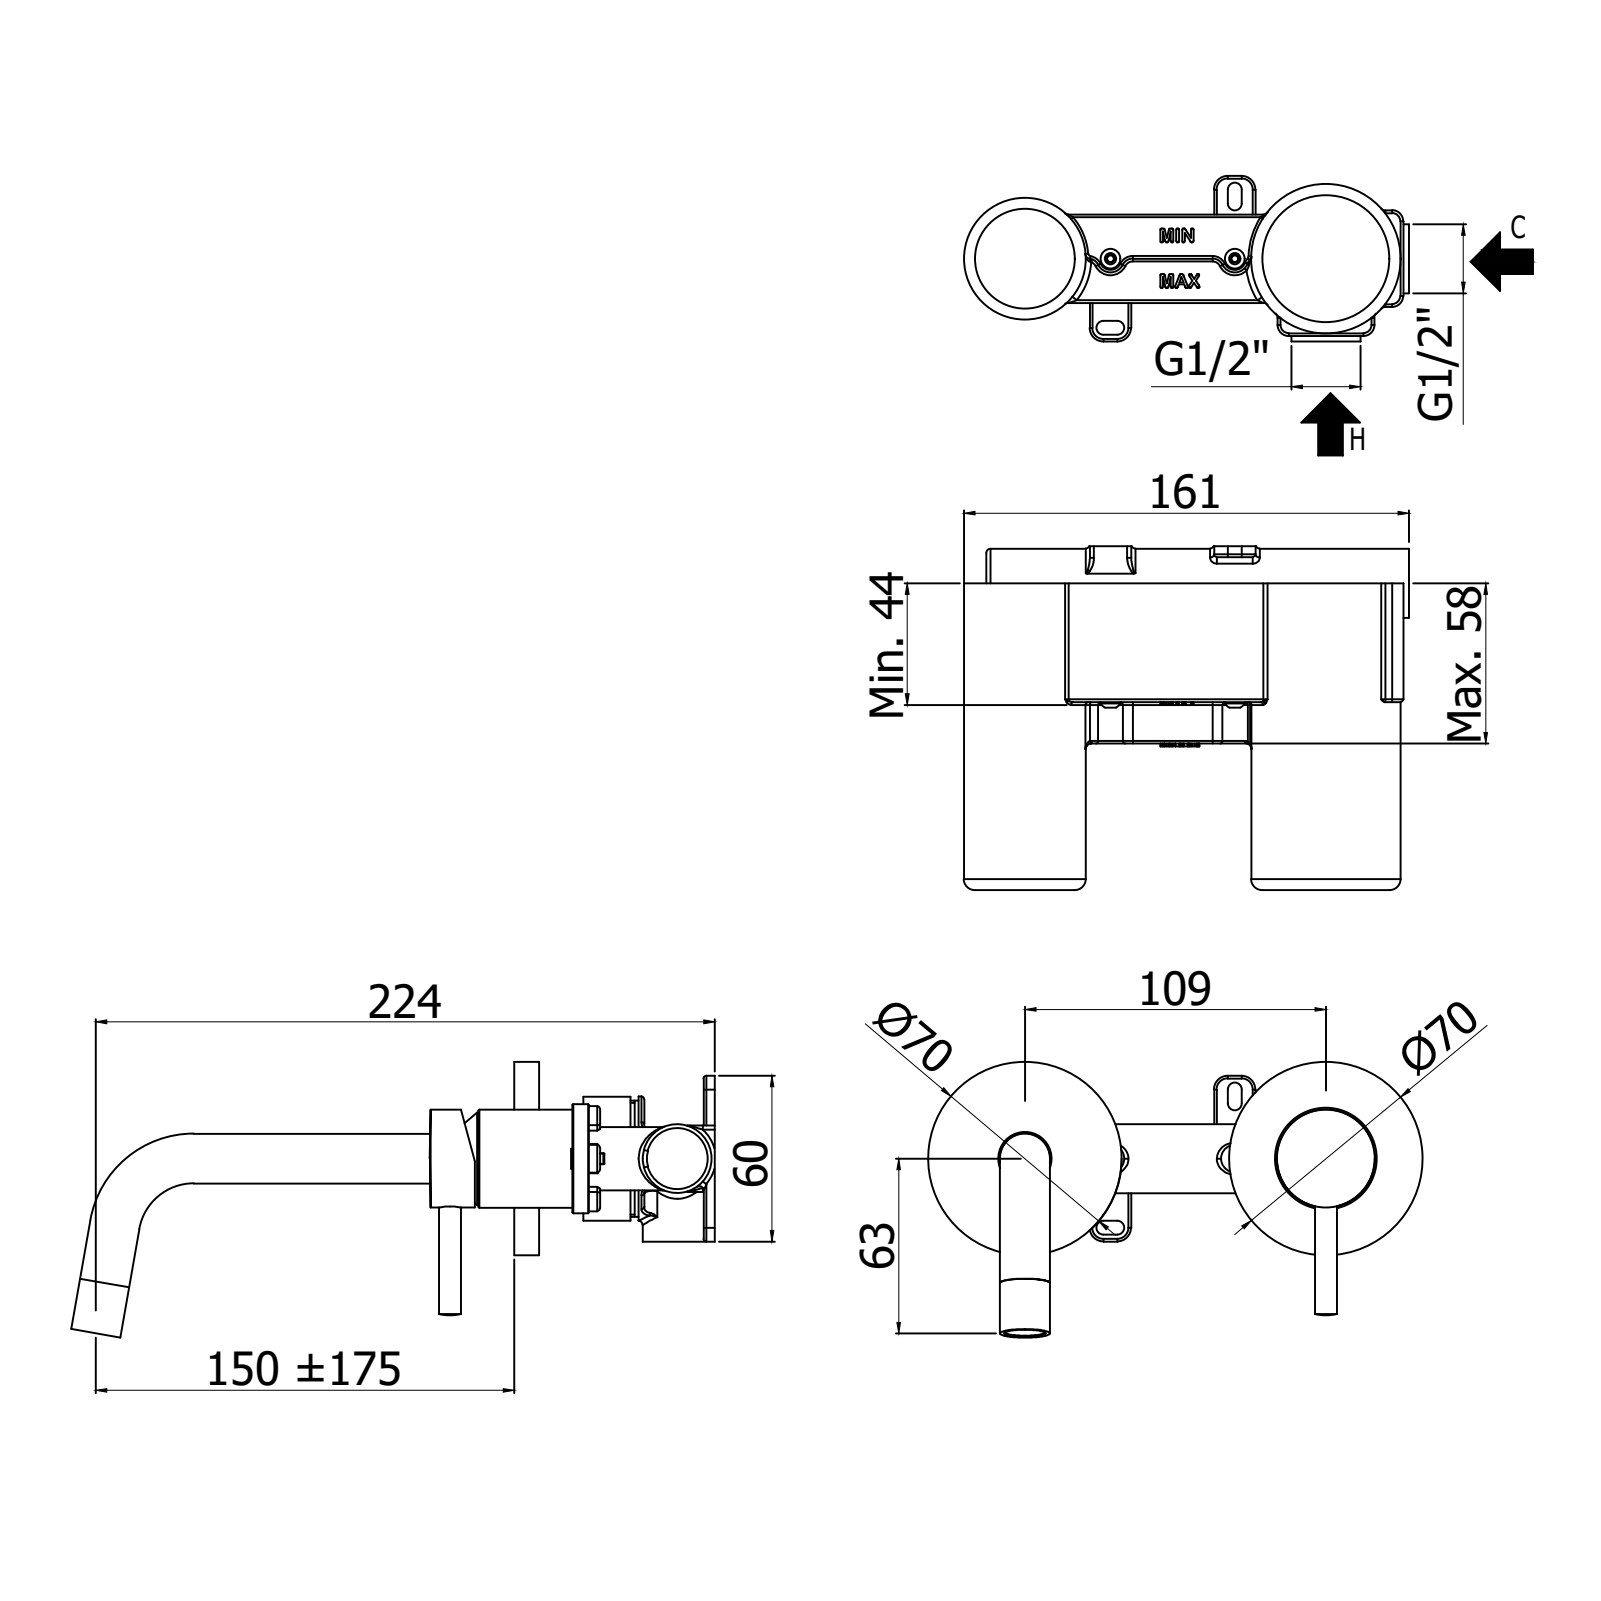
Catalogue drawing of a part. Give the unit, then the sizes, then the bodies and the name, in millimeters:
Units: millimetres
Overall size (bounding box): 179 × 174.38 × 99.78
Round holes (diameter × count): ⌀3.5 ×1, ⌀4.2 ×1, ⌀5.2 ×1, ⌀5.6 ×1, ⌀22.5 ×1, ⌀25.5 ×1, ⌀30 ×1, ⌀31.5 ×1
Round bosses / shafts (diameter × count): ⌀70 ×2, ⌀18 ×2, ⌀35.5 ×1, ⌀33.5 ×1, ⌀8 ×1
Partial cylindrical surfaces — rounded edges, fillets, slot ends (radius × count): R8.3 ×1
Main face-to-face distances: 9, 8.89, 8.78, 37.5, 37.39, 28.61, 28.5, 26, 25.89, 17.11
Hole centre spacings: 13.42
Volume: 130 308 mm³ · Surface area: 44 283 mm²
Bodies: 4 solids, 92 faces (26 planar, 40 cylindrical, 26 other)
Part name (STEP PRODUCT): LIG101CR70
STEP written by: CREO PARAMETRIC BY PTC INC, 2020044 (CONFIG_CONTROL_DESIGN)
